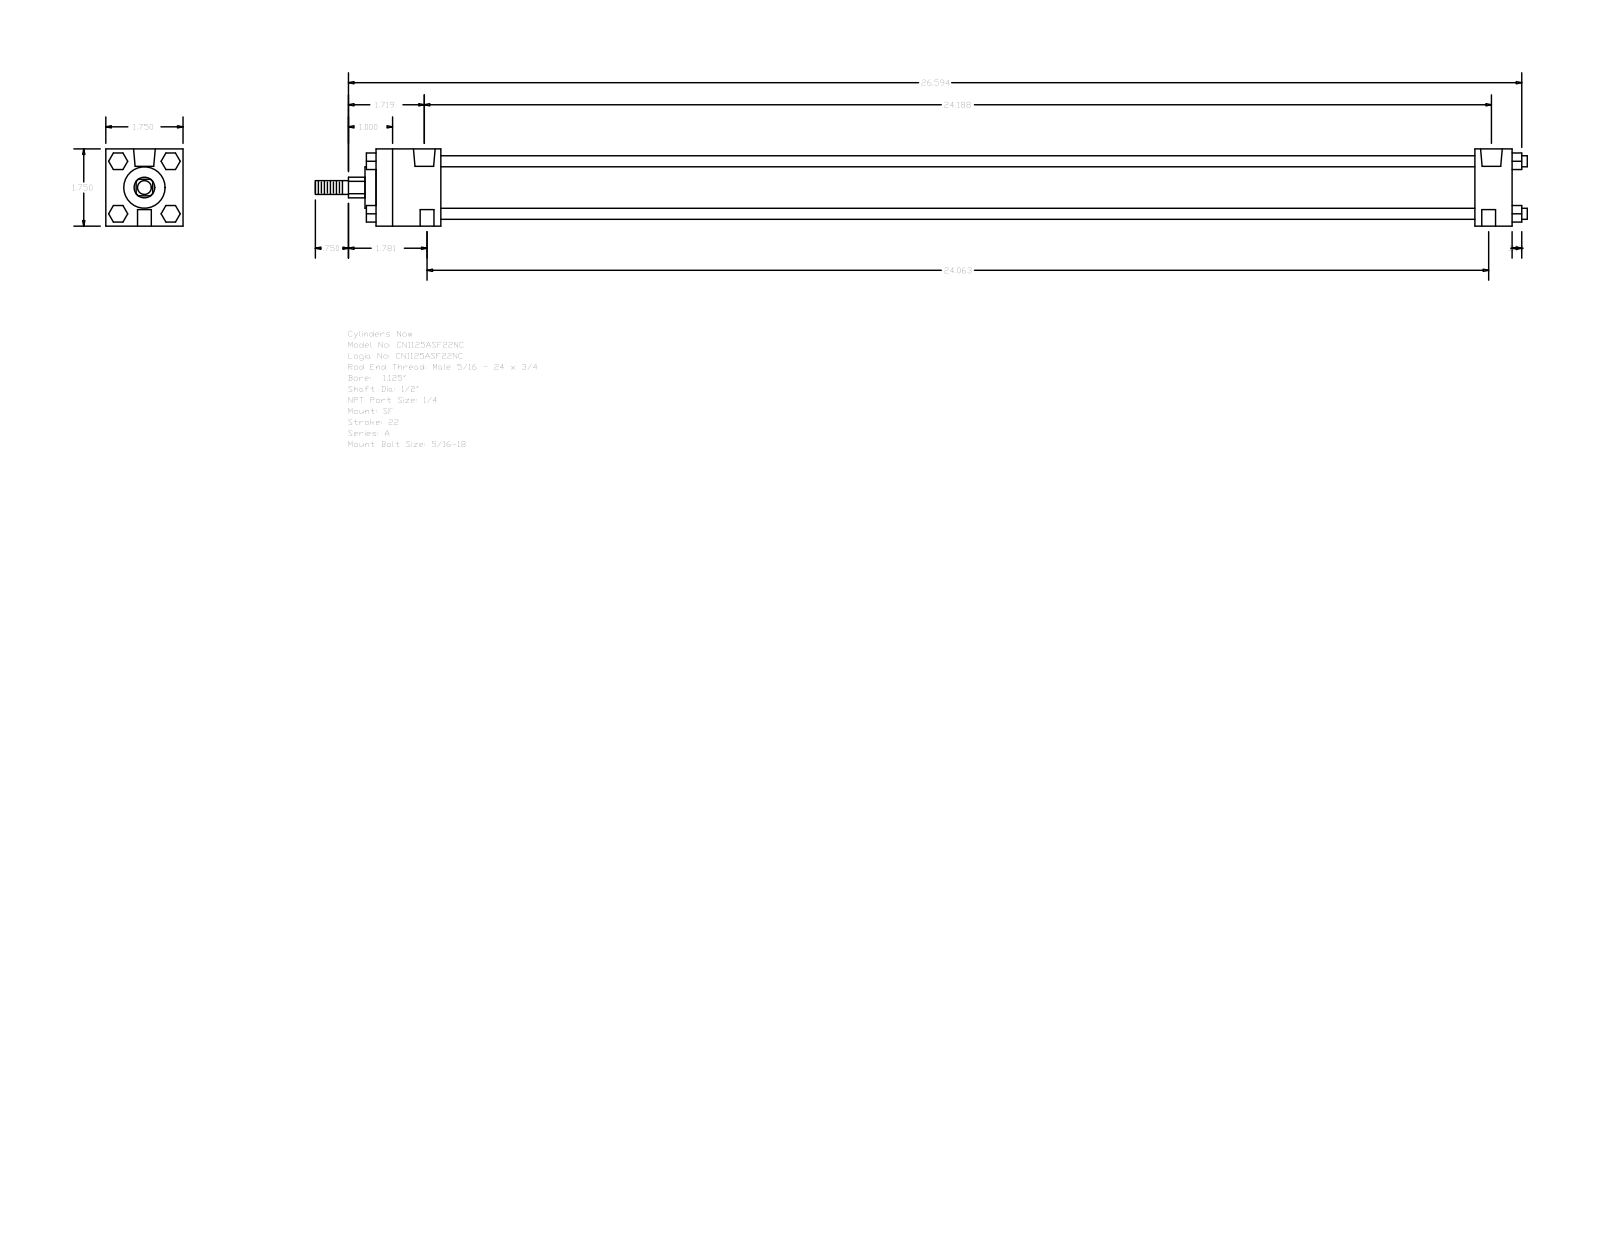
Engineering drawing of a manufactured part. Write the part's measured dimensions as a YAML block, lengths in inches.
part_name: "A_SF__0112_0.5"
step_written_by: "GSSL Pune (CONFIG_CONTROL_DESIGN)"
units: inches
bodies: {solids: 0, faces: 120, planar: 92, cylindrical: 28, other: 0}
overall_size: [27.469, 1.75, 1.75]
round_holes:
  - {diameter: 0.219, count: 2}
  - {diameter: 0.313, count: 2}
  - {diameter: 0.492, count: 2}
round_bosses_or_shafts:
  - {diameter: 0.25, count: 4}
  - {diameter: 1.255, count: 1}
  - {diameter: 0.937, count: 1}
  - {diameter: 0.5, count: 1}
  - {diameter: 0.313, count: 1}
partial_cylinders:
  - {radius: 0.234, count: 1}
face_to_face_distances: [1.75, 25.75, 24.906, 0.844, 1.469, 23.437, 24.281, 0.375, 0.22, 0.219]
hole_center_spacings: [24.063, 0.062, 0.063, 24.125, 24.125, 24.187]
